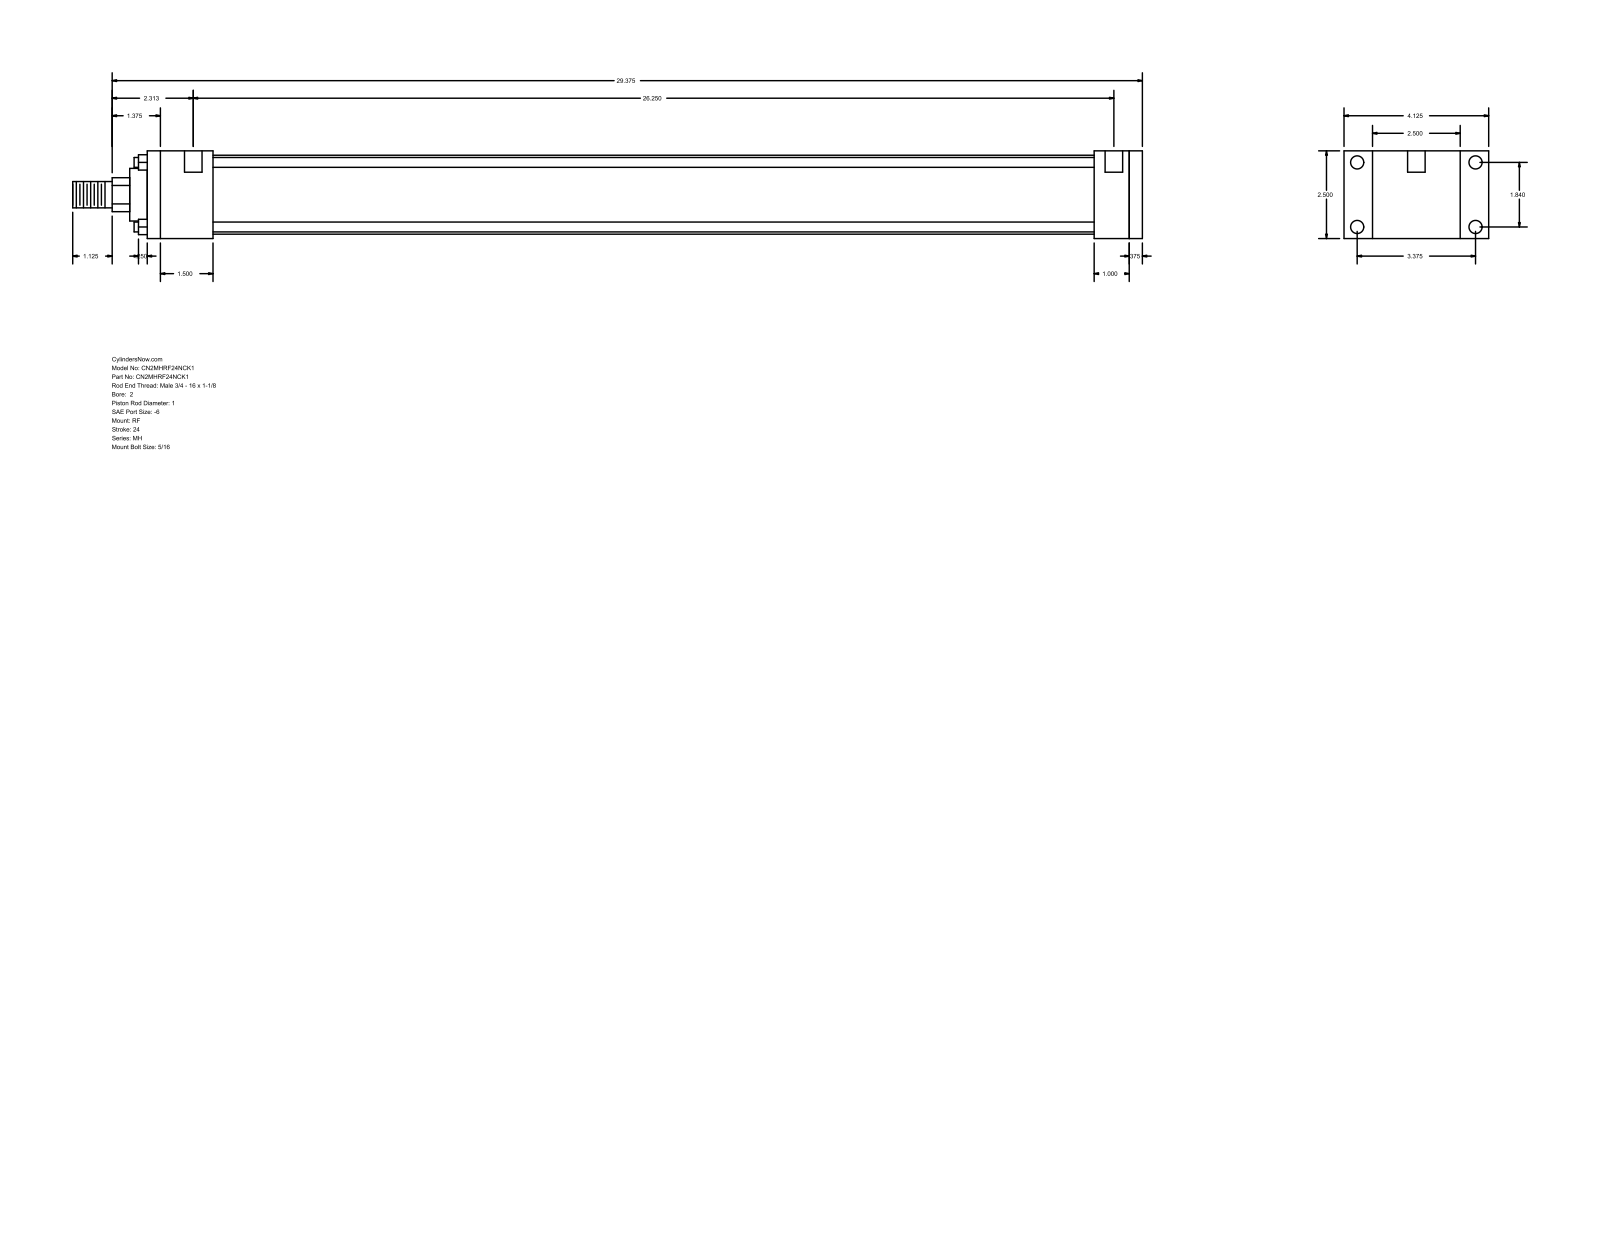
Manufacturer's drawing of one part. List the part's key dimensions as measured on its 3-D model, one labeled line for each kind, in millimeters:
Part name (STEP PRODUCT): MH_RF__0200_1
STEP written by: GSSL Pune (CONFIG_CONTROL_DESIGN)
Units: millimetres
Bodies: 0 solids, 92 faces (64 planar, 28 cylindrical, 0 other)
Overall size (bounding box): 774.7 × 104.78 × 63.5
Round holes (diameter × count): ⌀5.56 ×4, ⌀9.53 ×4, ⌀12.7 ×2
Round bosses / shafts (diameter × count): ⌀7.14 ×4, ⌀57.15 ×1, ⌀38.1 ×1, ⌀25.4 ×1, ⌀19.05 ×1
Partial cylindrical surfaces — rounded edges, fillets, slot ends (radius × count): R12.29 ×1
Main face-to-face distances: 63.5, 720.72, 9.52, 711.2, 20.64, 25.4, 47.63, 685.8, 638.17, 663.57
Hole centre spacings: 46.74, 85.72, 97.63, 674.68, 3.17, 4.76, 666.75, 669.92
